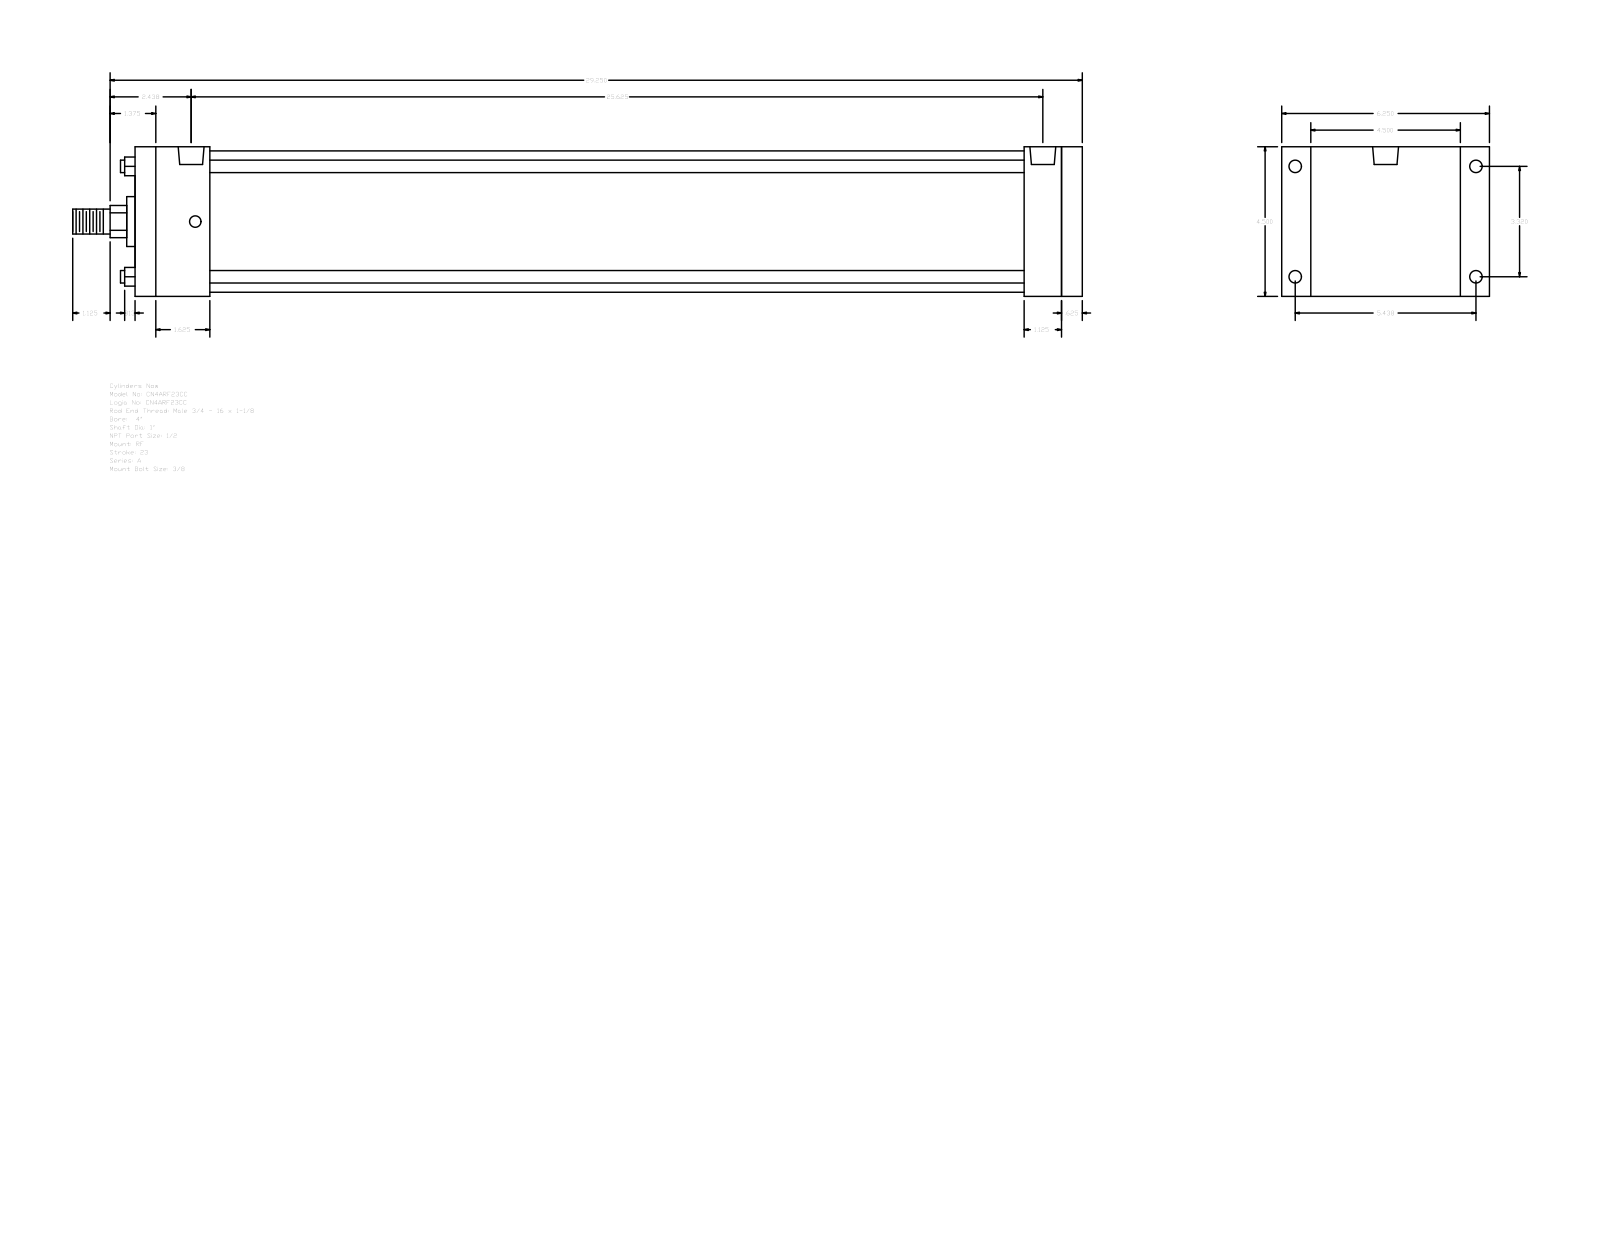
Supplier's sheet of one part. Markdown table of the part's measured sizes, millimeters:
| quantity | value |
| --- | --- |
| part name | A_RF__0400_1 |
| STEP written by | GSSL Pune (CONFIG_CONTROL_DESIGN) |
| units | millimeters |
| bodies | 0 solids, 92 faces (64 planar, 28 cylindrical, 0 other) |
| overall size | 771.52 × 158.75 × 114.3 |
| round holes (diameter × count) | 8.73 × 4, 9.53 × 4, 19.77 × 2 |
| round bosses / shafts (diameter × count) | 9.53 × 4, 107.95 × 1, 38.1 × 1, 25.4 × 1, 19.05 × 1 |
| partial cylindrical surfaces (radius × count) | 12.29 × 1 |
| main face-to-face distances | 114.3, 723.9, 708.03, 15.87, 22.23, 136.53, 679.45, 28.58, 44.45, 57.15 |
| hole center spacings | 3.18, 84.32, 138.12, 161.82, 644.52, 647.7, 650.88 |
